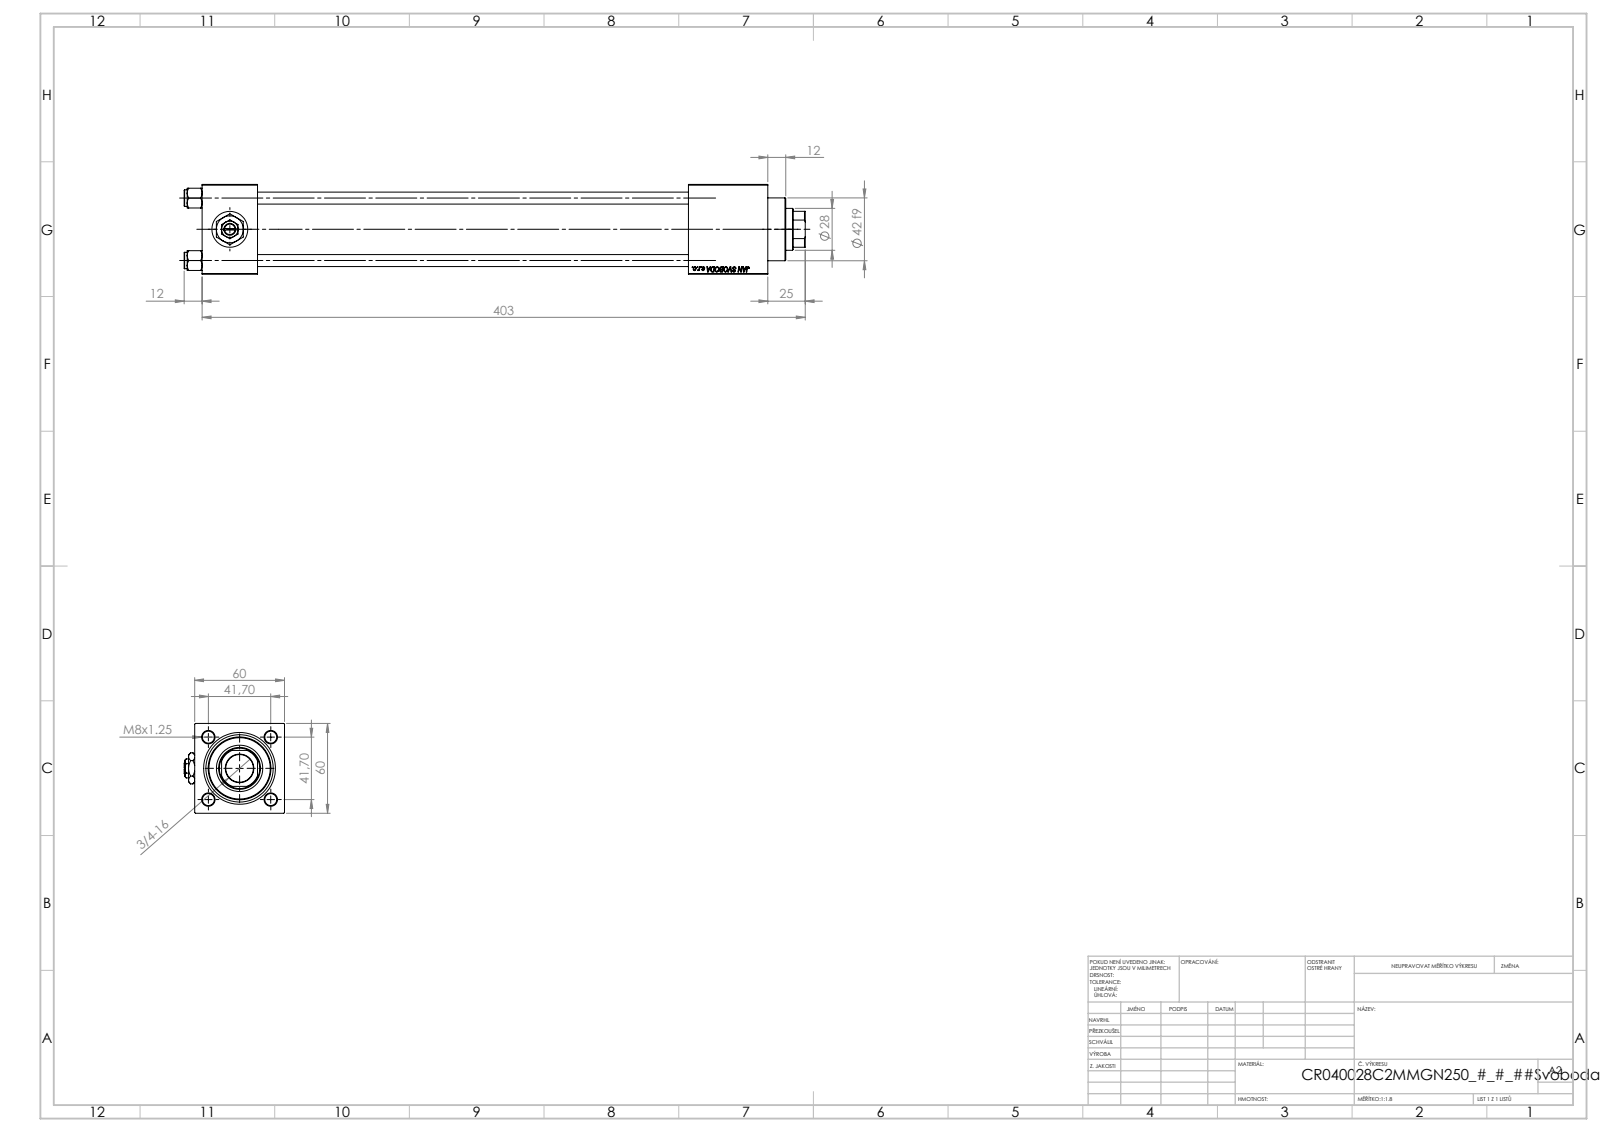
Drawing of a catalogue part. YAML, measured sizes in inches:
part_name: "V215CR_C_TYCINKA; V215_VC_A; V215CR_C_Body; Zatka_pro_OIL_PORT (+2 more)"
step_written_by: "SolidWorks 2019 (CONFIG_CONTROL_DESIGN)"
units: inches
bodies: {solids: 12, faces: 1202, planar: 550, cylindrical: 94, other: 558}
overall_size: [16.339, 2.638, 2.362]
volume: 42.95
surface_area: 338.8
round_holes:
  - {diameter: 0.315, count: 4}
  - {diameter: 0.276, count: 2}
  - {diameter: 0.656, count: 2}
  - {diameter: 0.945, count: 2}
  - {diameter: 0.728, count: 1}
  - {diameter: 1.102, count: 1}
  - {diameter: 1.22, count: 1}
  - {diameter: 1.575, count: 1}
  - {diameter: 1.772, count: 1}
round_bosses_or_shafts:
  - {diameter: 0.433, count: 4}
  - {diameter: 1.811, count: 1}
  - {diameter: 1.654, count: 1}
partial_cylinders:
  - {radius: 0.531, count: 1}
face_to_face_distances: [2.362, 1.457, 12.795, 11.339, 13.752, 12.295, 0.957, 2.087, 14.882, 13.425]
hole_center_spacings: [1.161, 1.642, 2.322, 12.697]
